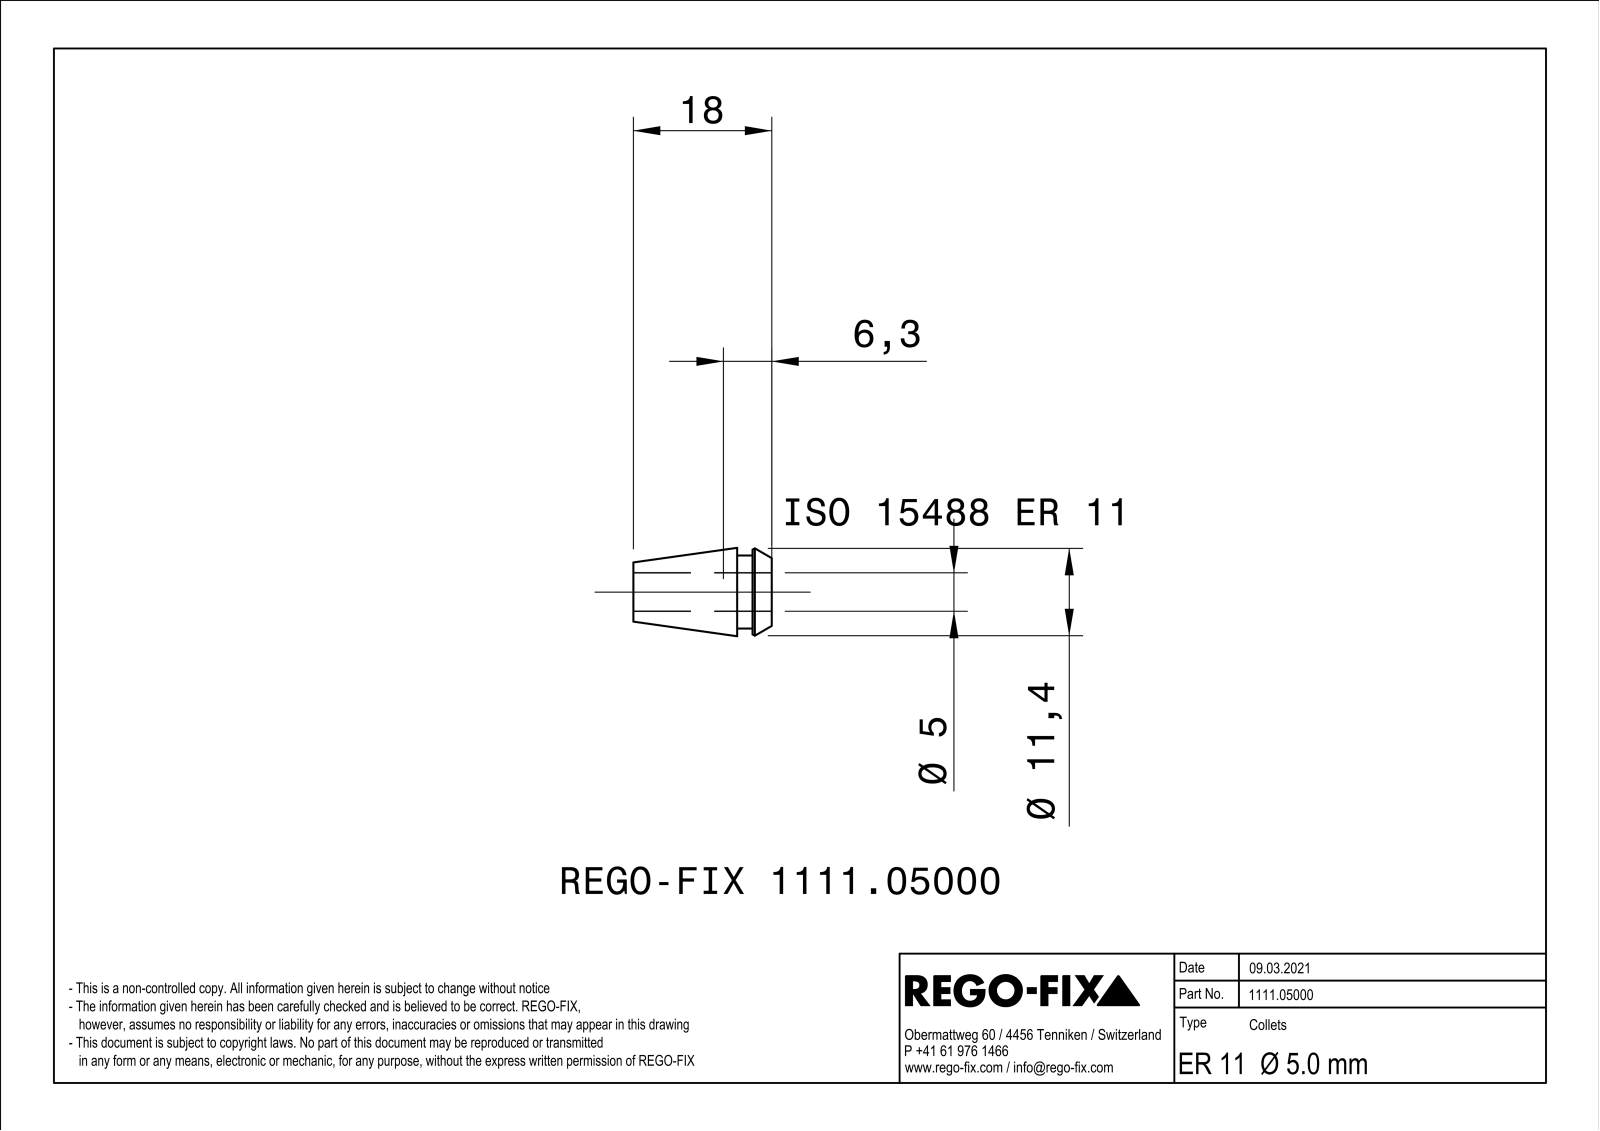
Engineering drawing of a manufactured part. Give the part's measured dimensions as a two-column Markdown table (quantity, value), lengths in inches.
| quantity | value |
| --- | --- |
| part name | NOCUT |
| STEP written by | SIEMENS PLM Software Solid Edge ST10 (AUTOMOTIVE_DESIGN) |
| units | inches |
| bodies | 1 solid, 157 faces (66 planar, 37 cylindrical, 54 other) |
| overall size | 0.709 × 0.453 × 0.452 |
| volume | 0.049 in³ |
| surface area | 2.527 in² |
| round holes (diameter × count) | 0.197 × 1 |
| round bosses / shafts (diameter × count) | 0.453 × 1, 0.374 × 1 |
| partial cylindrical surfaces (radius × count) | 0.984 × 12 |
| main face-to-face distances | 0.018, 0.018, 0.017, 0.098, 0.177, 0.079, 0.709, 0.61, 0.531, 0.157 |
